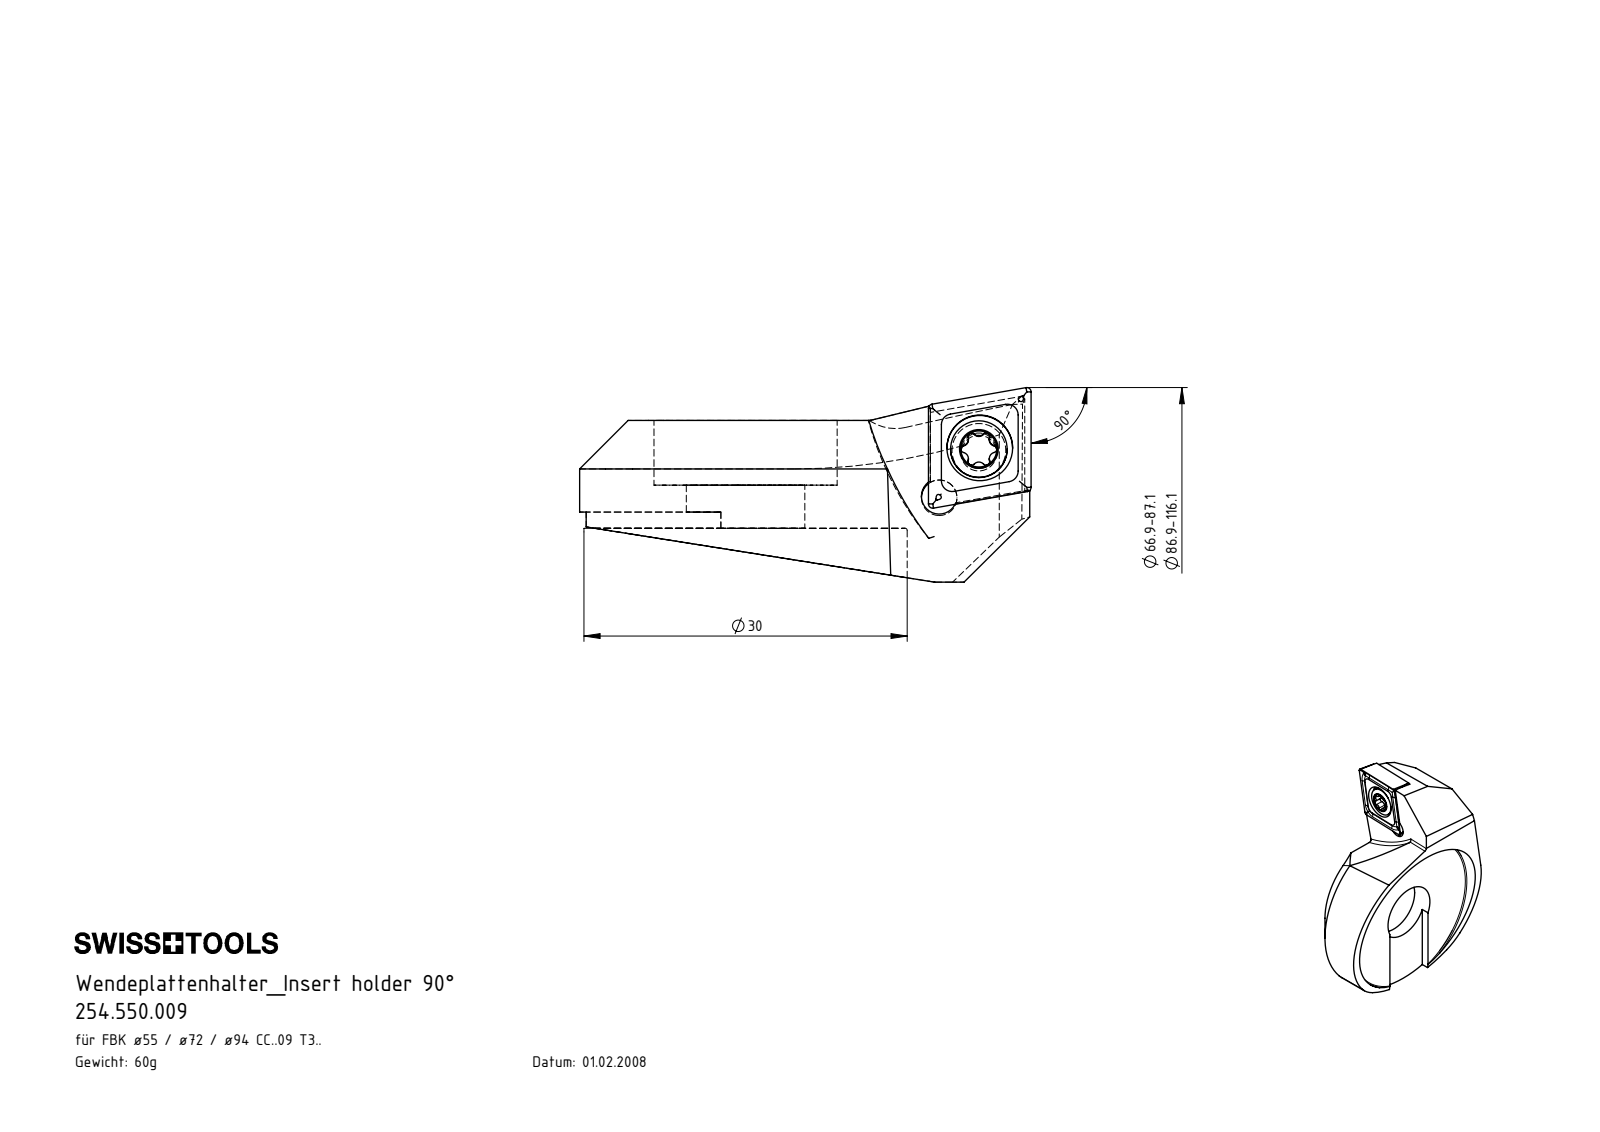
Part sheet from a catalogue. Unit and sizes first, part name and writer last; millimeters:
Units: millimetres
Overall size (bounding box): 41.9 × 33.1 × 18.05
Round holes (diameter × count): ⌀3.3 ×2, ⌀4.4 ×1, ⌀6.1 ×1, ⌀11 ×1, ⌀17 ×1, ⌀30 ×1
Round bosses / shafts (diameter × count): ⌀5.25 ×1, ⌀4 ×1
Partial cylindrical surfaces — rounded edges, fillets, slot ends (radius × count): R0.34 ×6, R0.59 ×6, R0.5 ×2, R10 ×2, R5 ×1, R16.55 ×1, R20.9 ×1, R30 ×1
Main face-to-face distances: 10, 6, 4, 8.5, 2.5, 1.5, 3.77, 9, 15, 6.5
Hole centre spacings: 5.73, 5.87
Volume: 7 697 mm³ · Surface area: 4 246 mm²
Bodies: 3 solids, 146 faces (41 planar, 45 cylindrical, 60 other)
Part name (STEP PRODUCT): WCB-ER2.001.009_A; F55-WCB.001.013_D_fertigbearbeitet; 254.550.009; CCMT09T304
STEP written by: SolidWorks 2017 (CONFIG_CONTROL_DESIGN)
